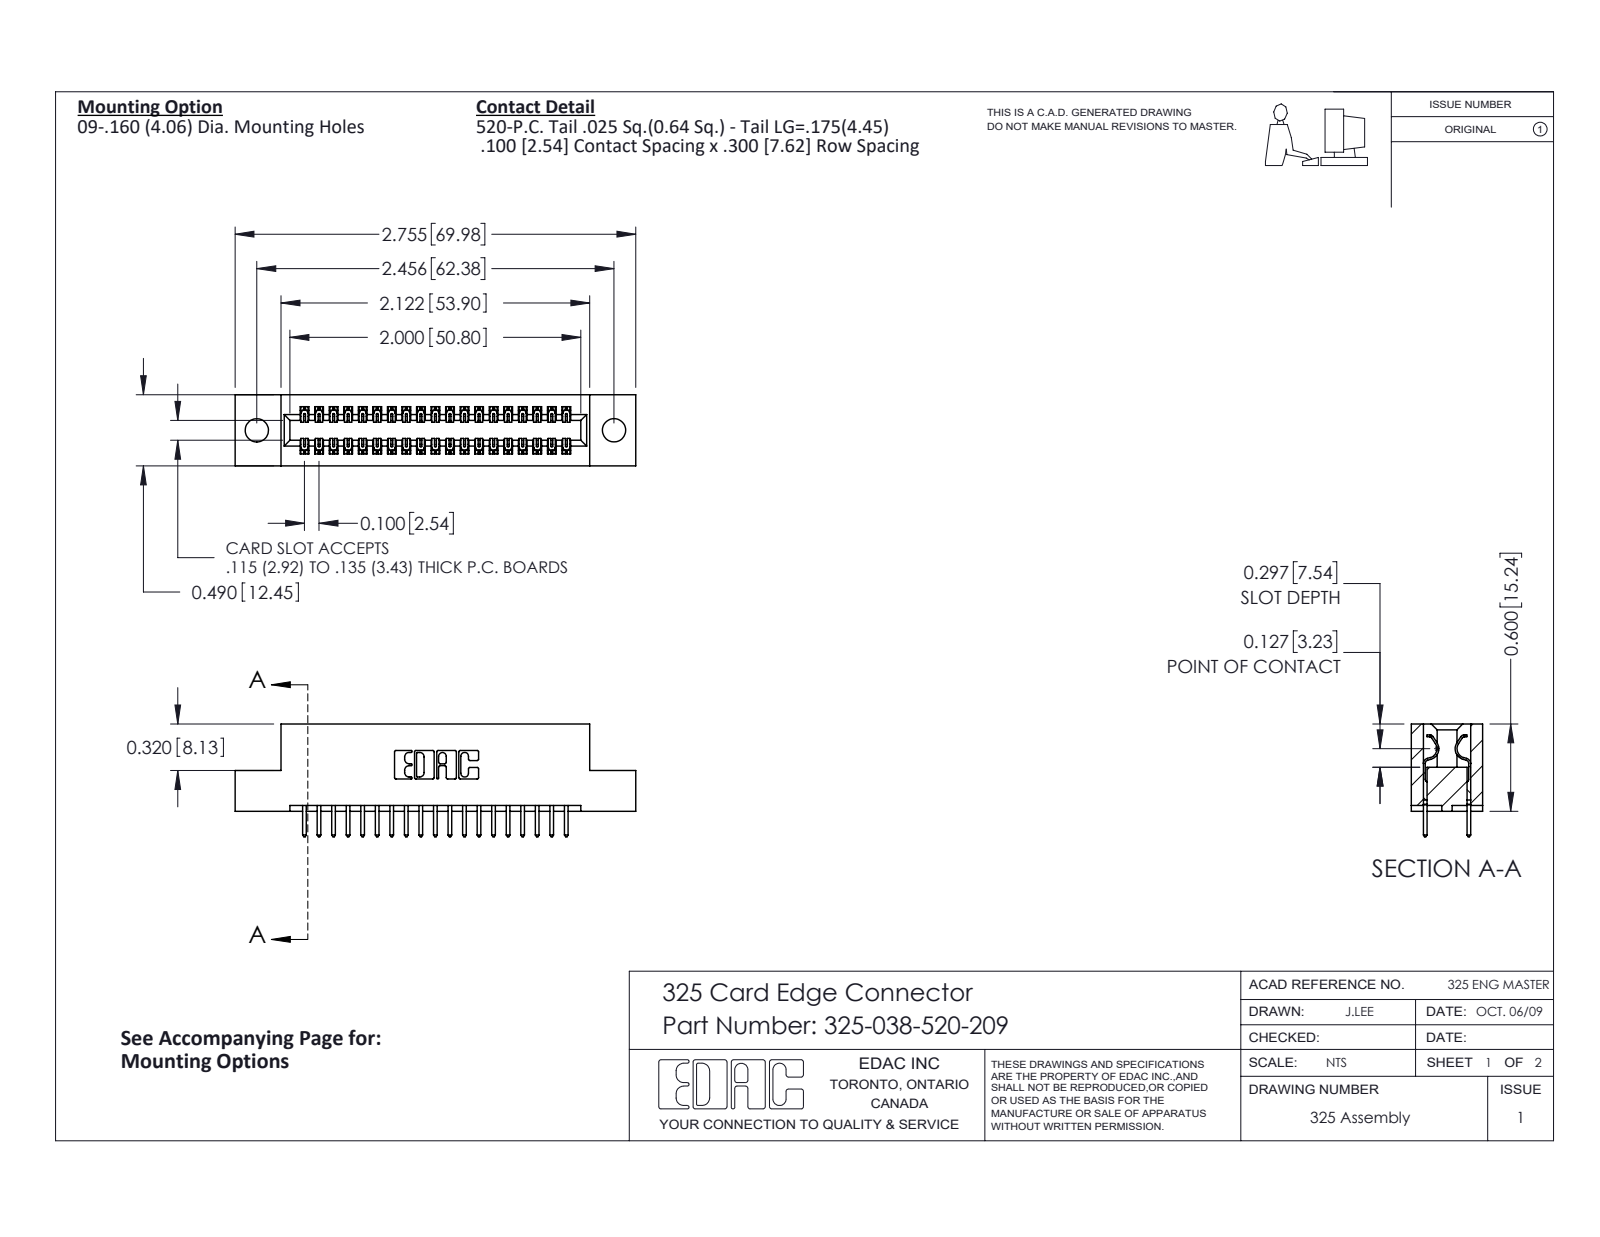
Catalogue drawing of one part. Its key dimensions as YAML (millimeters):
part_name: "325-292-001_325-293-120; 325-038-520-209; 325 Part_.160 TH"
step_written_by: "SolidWorks 2016 (CONFIG_CONTROL_DESIGN)"
units: millimeters
bodies: {solids: 39, faces: 2090, planar: 1438, cylindrical: 652, other: 0}
overall_size: [70, 19.7, 12.4]
volume: 8590
surface_area: 9697
round_holes:
  - {diameter: 4.1, count: 2}
partial_cylinders:
  - {radius: 0.2, count: 57}
  - {radius: 0.3, count: 38}
  - {radius: 0.3, count: 22}
  - {radius: 0.2, count: 6}
  - {radius: 0.8, count: 6}
  - {radius: 0.7, count: 3}
  - {radius: 0.4, count: 2}
  - {radius: 0.6, count: 2}
face_to_face_distances: [2.1, 10.3, 7.6, 12.4, 2.7, 9.7, 0.6, 8.3, 1, 2.5]
hole_center_spacings: [62.4]
